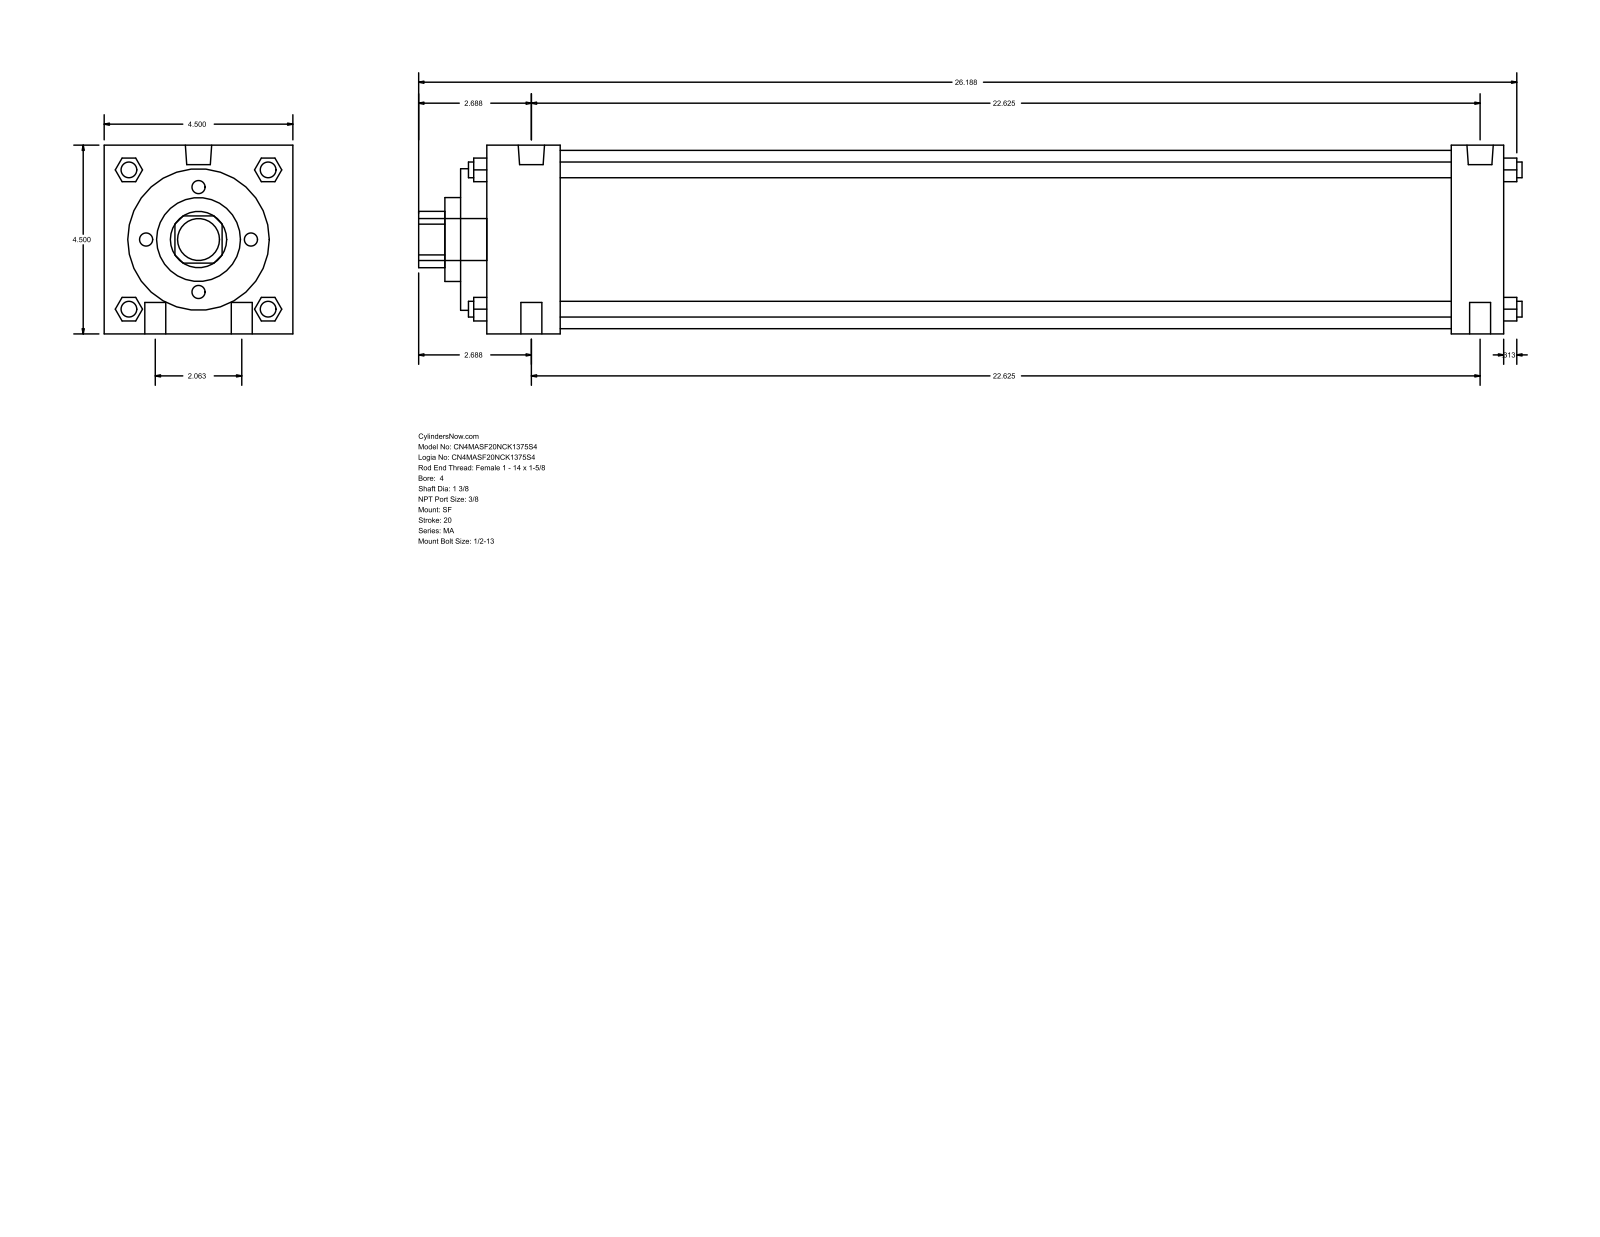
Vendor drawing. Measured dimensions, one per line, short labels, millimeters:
name: MA_SF__0400_1.375
written by: GSSL Pune (CONFIG_CONTROL_DESIGN)
unit: mm
bodies: 0 solids, 126 faces (95 planar, 31 cylindrical, 0 other)
size: 668.34 × 114.3 × 114.3
holes: 1× ⌀34.92, 1× ⌀50.8, 1× ⌀85.72, 1× ⌀107.95
bosses: 4× ⌀12.7, 4× ⌀9.53, 2× ⌀15.93, 2× ⌀11.11, 1× ⌀25.4
rounds: 1× R17.06
face distances: 114.3, 615.96, 15.87, 631.83, 600.08, 584.21, 31.75, 60.32, 44.45, 539.76
